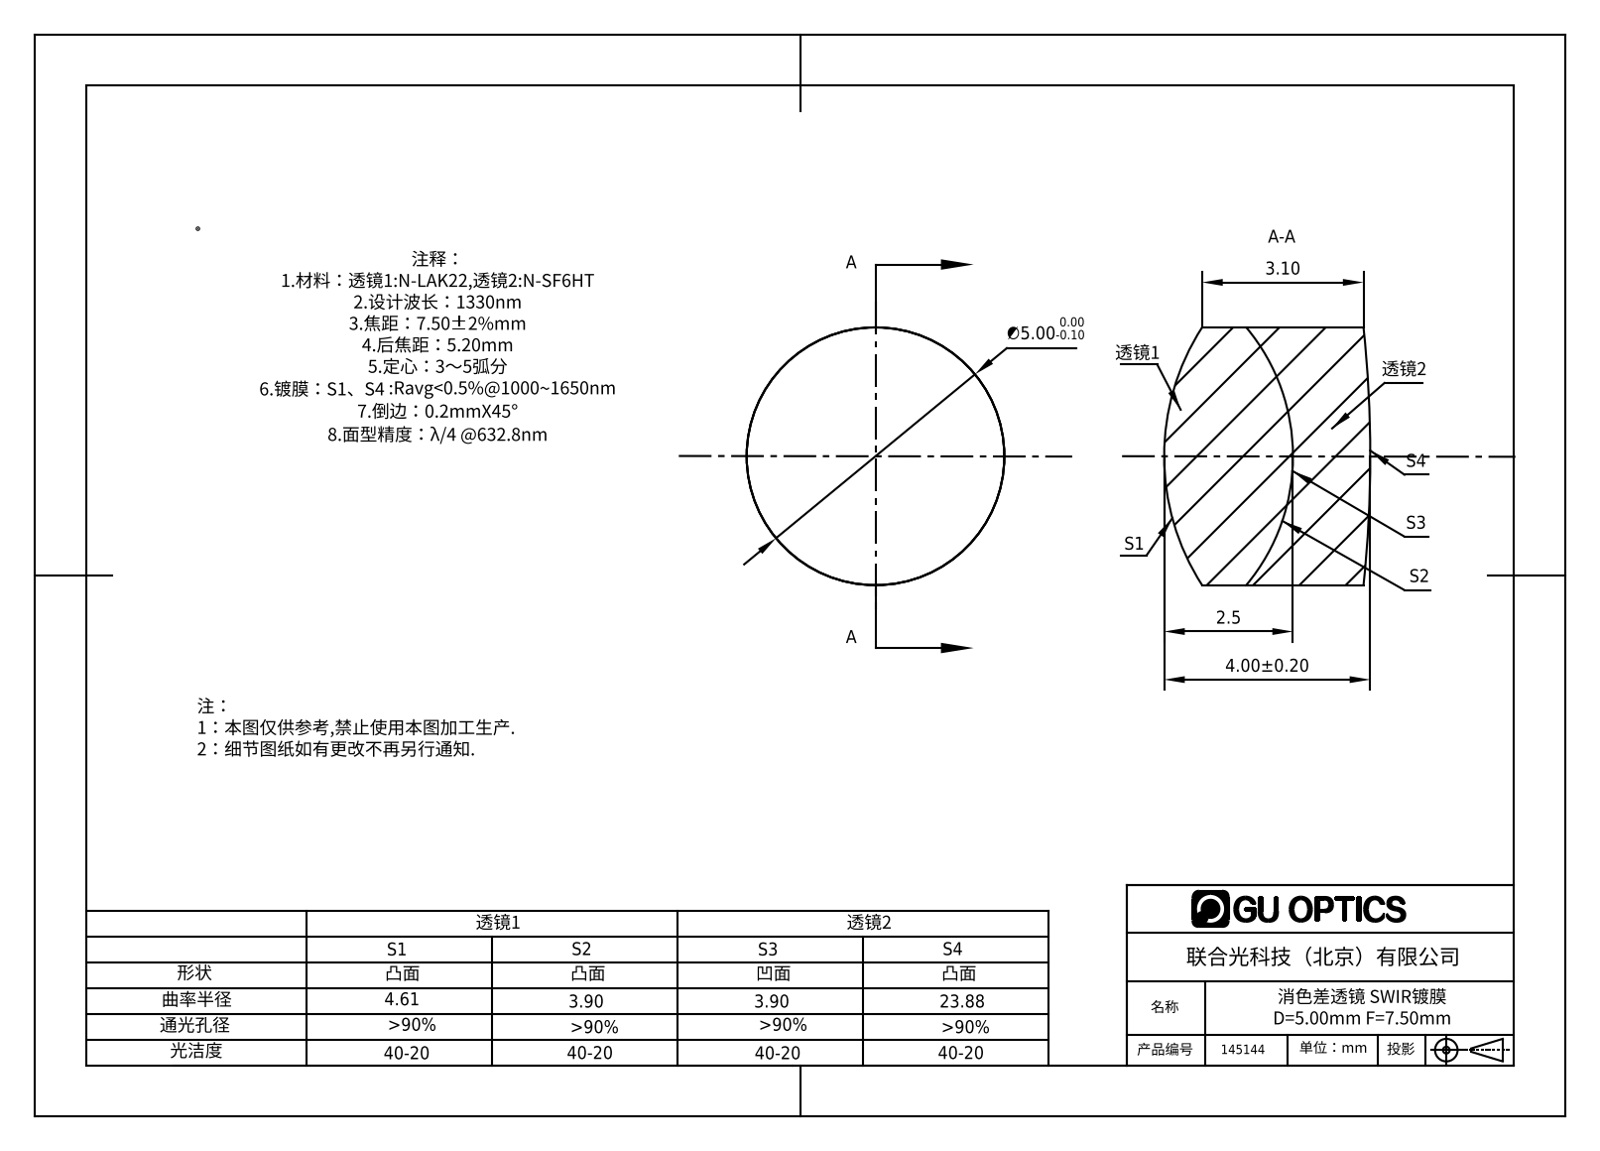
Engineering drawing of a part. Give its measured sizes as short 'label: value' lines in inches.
name: 145144
written by: SolidWorks 2016 (AUTOMOTIVE_DESIGN)
unit: in
bodies: 2 solids, 12 faces (0 planar, 4 cylindrical, 8 other)
size: 0.197 × 0.197 × 0.157
volume: 0.004 in³; area: 0.209 in²
bosses: 1× ⌀0.197
